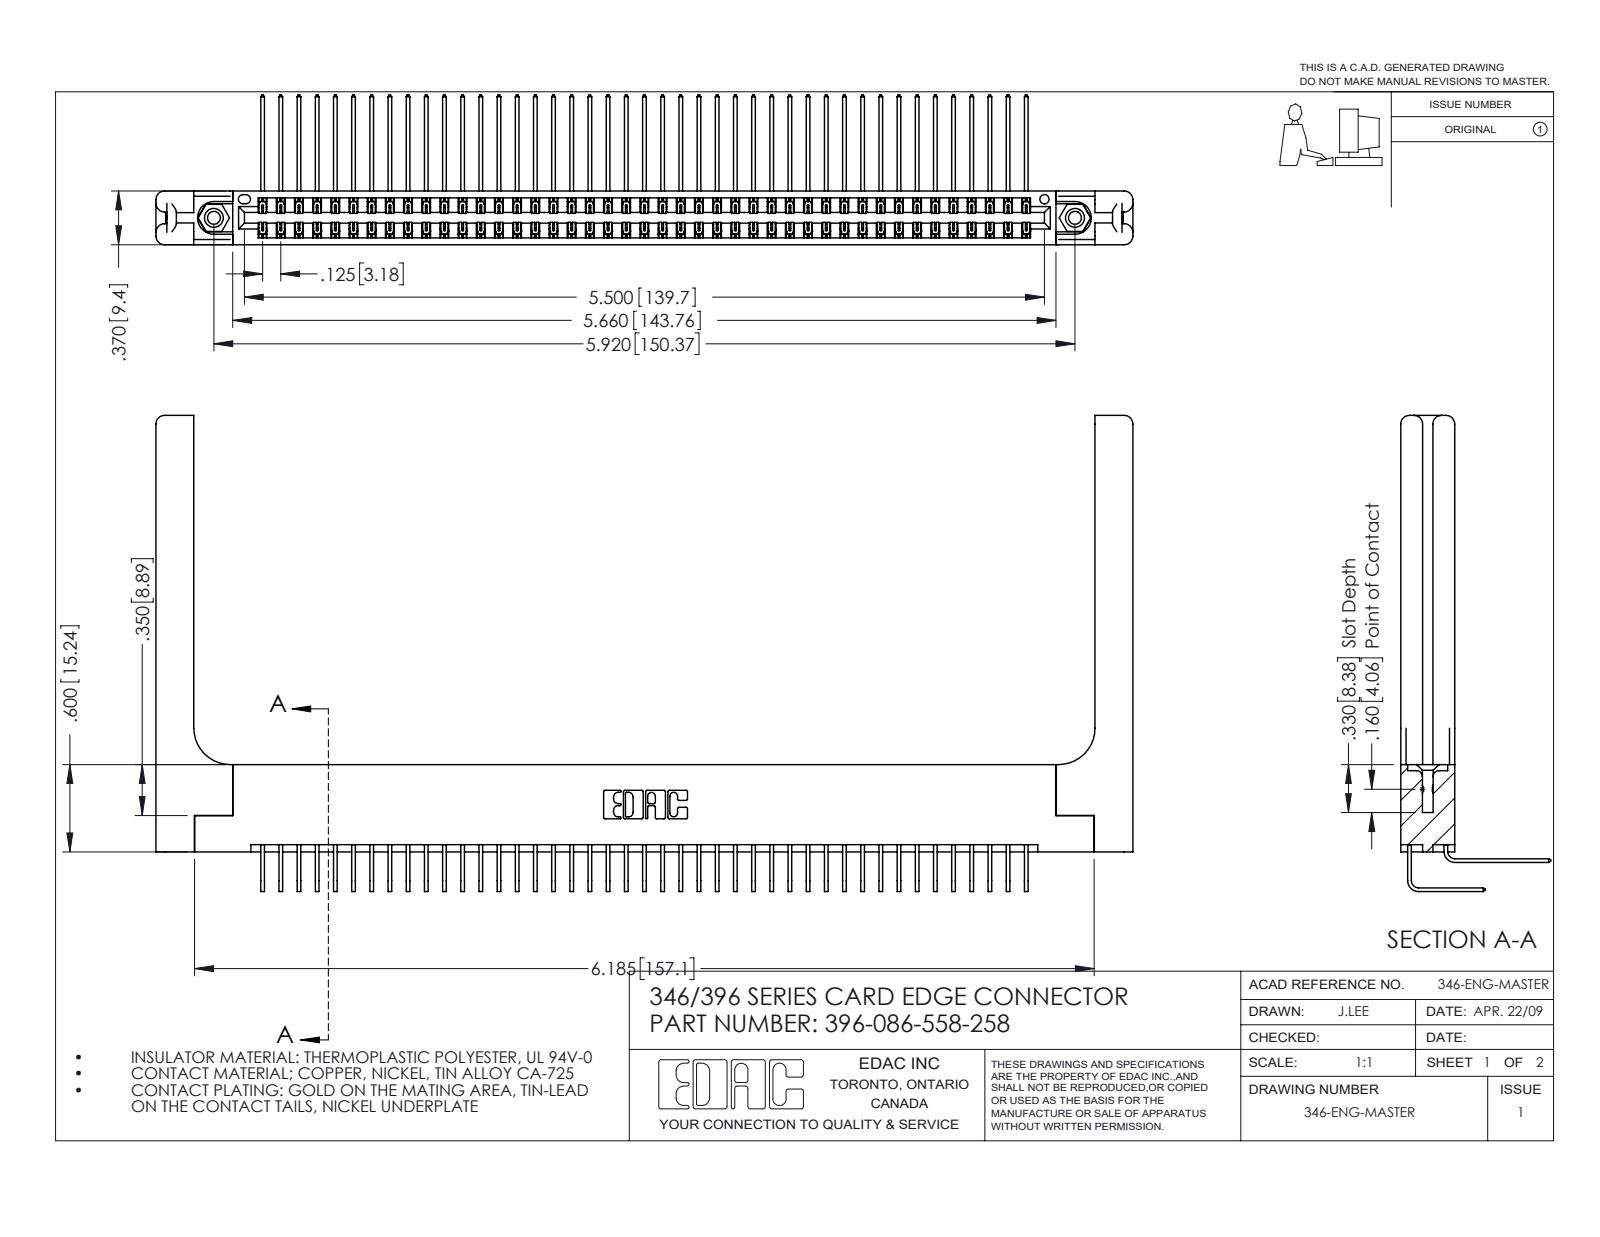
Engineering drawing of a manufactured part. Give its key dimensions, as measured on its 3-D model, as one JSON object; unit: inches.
{"part_name": "345-250-001_345-250-001-102; 345-292-001_558 559 Tail - 1; 346 Part_Flush Mounting Lugs - 0.156 Dia-TH; 346-220-058_345-220-058 (+2 more)", "step_written_by": "SolidWorks 2016 (CONFIG_CONTROL_DESIGN)", "units": "inches", "bodies": {"solids": 91, "faces": 5022, "planar": 3406, "cylindrical": 1556, "other": 60}, "overall_size": [6.716, 3.273, 1.03], "volume_in3": 1.503, "surface_area_in2": 47.94, "round_holes": [[0.089, 2], [0.125, 2], [0.156, 2], [0.064, 1]], "round_bosses_or_shafts": [[0.155, 2]], "partial_cylinders_radius": [[0.006, 129], [0.01, 22], [0.06, 16], [0.007, 6], [0.031, 6], [0.026, 3], [0.014, 2], [0.022, 2]], "face_to_face_distances": [0.322, 0.048, 0.37, 0.072, 0.025, 0.298, 0.25, 0.148, 0.15, 0.275], "hole_center_spacings": [0.246, 5.711, 5.92]}
